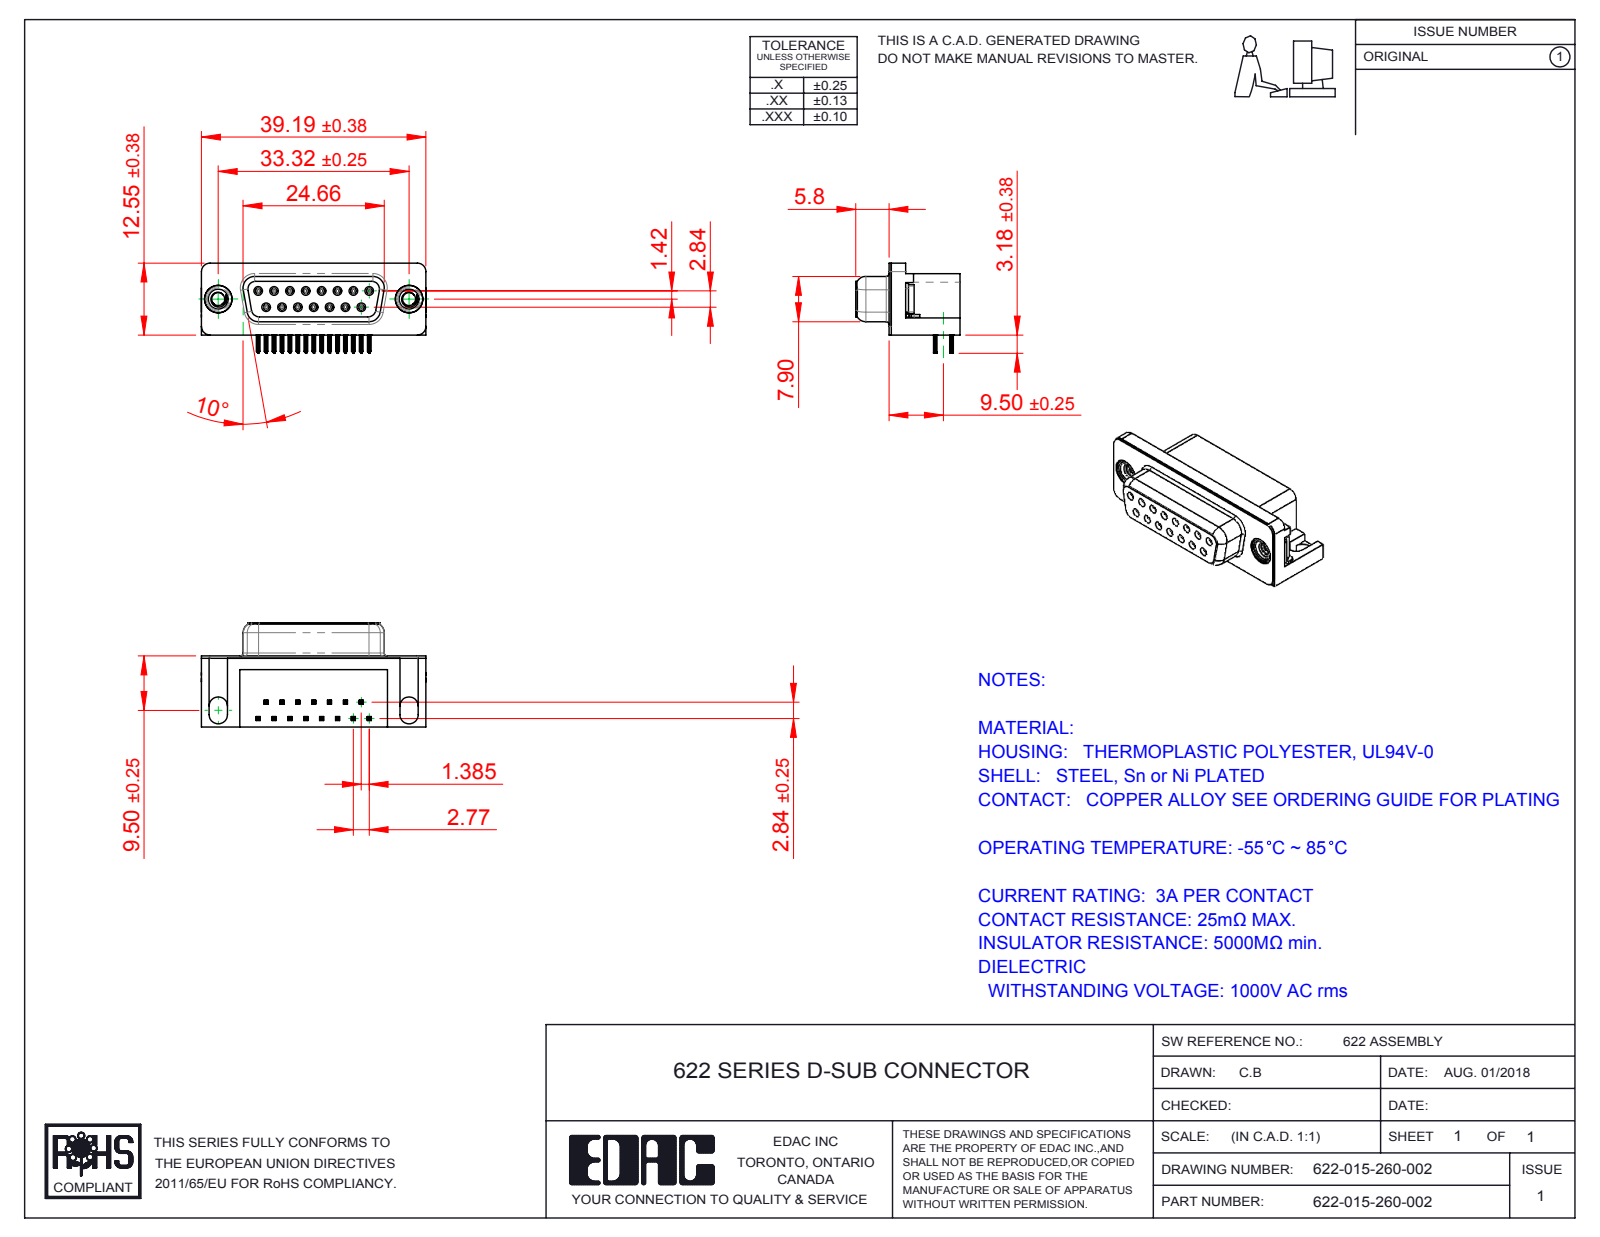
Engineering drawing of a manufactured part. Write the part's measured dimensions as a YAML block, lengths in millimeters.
part_name: "622-015-260-002; 622 Non Board Mount; 622 Housing_15 Socket; 622 Shell_15 Socket (+3 more)"
step_written_by: "SolidWorks 2016 (CONFIG_CONTROL_DESIGN)"
units: millimeters
bodies: {solids: 21, faces: 2423, planar: 1074, cylindrical: 601, other: 748}
overall_size: [39.22, 18.2, 15.73]
volume: 5153
surface_area: 6543
round_holes:
  - {diameter: 0.8, count: 15}
  - {diameter: 0.9, count: 15}
  - {diameter: 2.26, count: 2}
  - {diameter: 4, count: 2}
  - {diameter: 4.8, count: 2}
  - {diameter: 5, count: 2}
round_bosses_or_shafts:
  - {diameter: 1.2, count: 15}
  - {diameter: 4.9, count: 2}
  - {diameter: 4.75, count: 2}
  - {diameter: 3.9, count: 2}
partial_cylinders:
  - {radius: 0.1, count: 120}
  - {radius: 0.15, count: 60}
  - {radius: 0.35, count: 30}
  - {radius: 1, count: 18}
  - {radius: 0.34, count: 15}
  - {radius: 0.25, count: 8}
  - {radius: 1.35, count: 8}
  - {radius: 1.5, count: 8}
face_to_face_distances: [0.4, 12, 6.2, 12.4, 10.35, 2.9, 9.5, 2.5, 0.35, 0.45]
hole_center_spacings: [3.16, 2.77, 5.54, 8.31, 11.08, 5.03, 5.04, 7.48]
